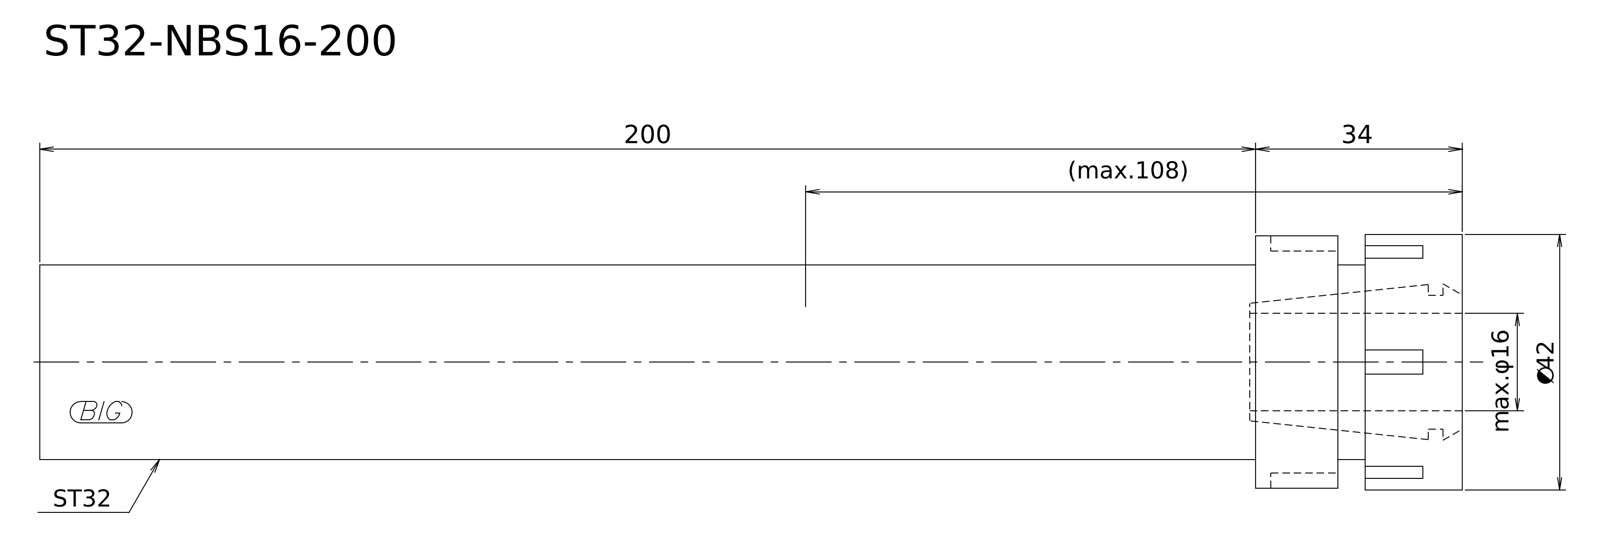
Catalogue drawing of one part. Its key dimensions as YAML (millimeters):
step_written_by: "Kubotek KeyCreator V8.5.1 (14335) (CONFIG_CONTROL_DESIGN)"
units: millimeters
bodies: {solids: 1, faces: 9, planar: 5, cylindrical: 4, other: 0}
overall_size: [234, 42, 42]
volume: 204897
surface_area: 28298
round_bosses_or_shafts:
  - {diameter: 42, count: 1}
  - {diameter: 41.5, count: 1}
  - {diameter: 32, count: 1}
face_to_face_distances: [234, 16, 218, 20.5, 4.5, 213.5, 34, 18, 13.5, 200]
